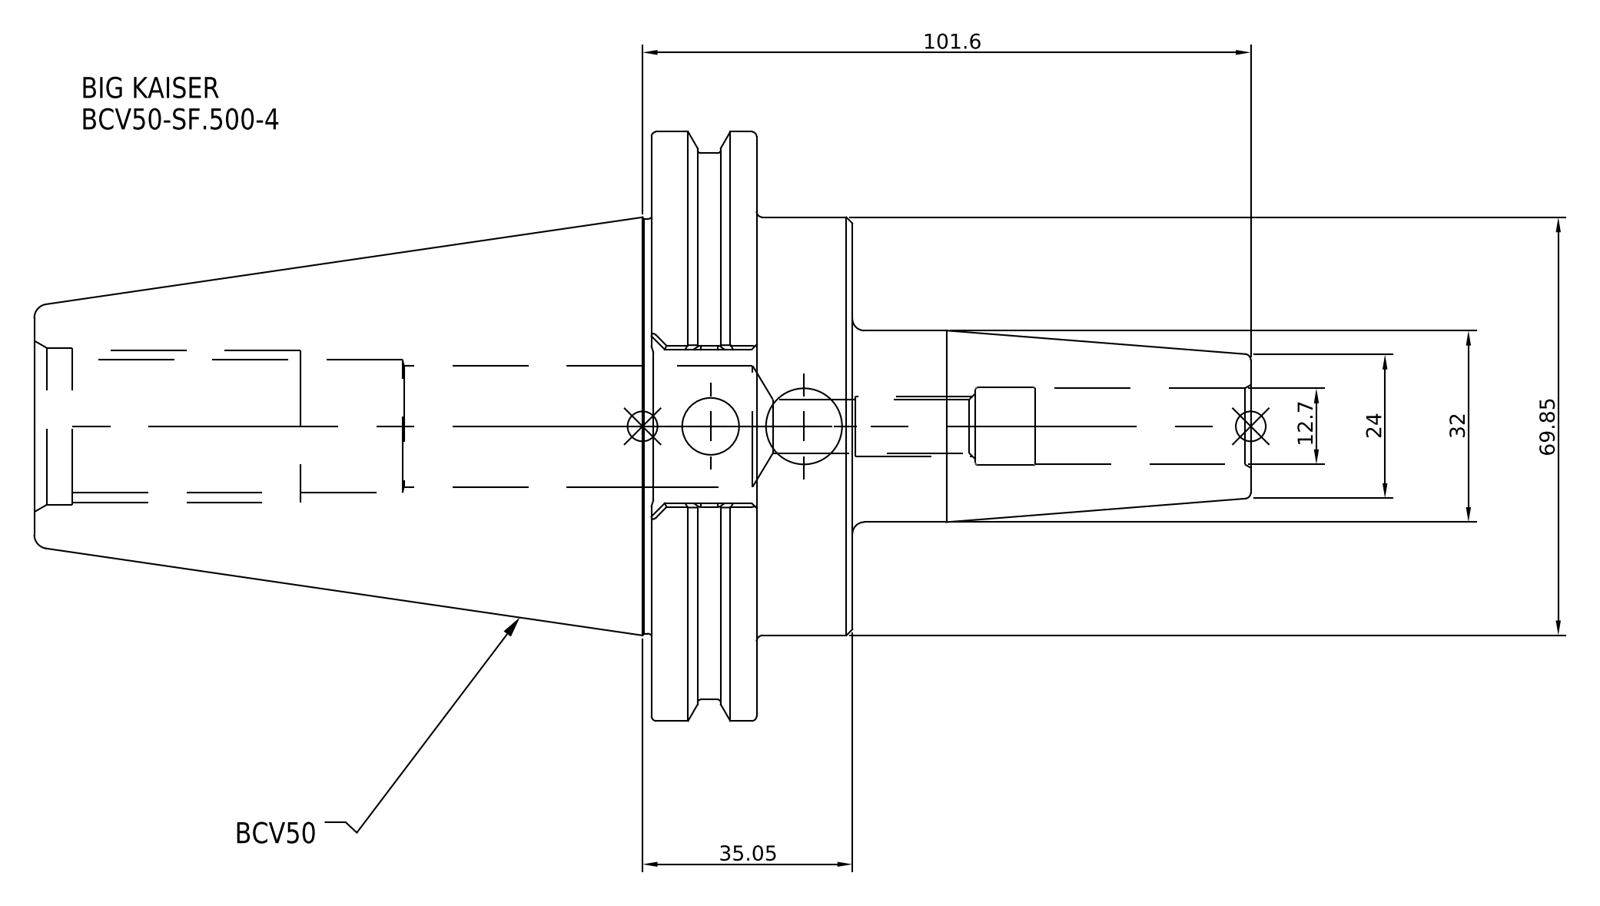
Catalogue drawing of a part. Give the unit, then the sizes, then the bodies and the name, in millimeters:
Units: millimetres
Overall size (bounding box): 203.2 × 98.43 × 98.43
Round holes (diameter × count): ⌀12.7 ×1
Round bosses / shafts (diameter × count): ⌀98.43 ×1, ⌀91.29 ×1, ⌀69.85 ×1, ⌀32 ×1
Main face-to-face distances: 17.55, 16, 33.55, 136.65, 120.65, 103.1, 66.55, 82.55, 100.1, 203.2
Volume: 482 267 mm³ · Surface area: 48 134 mm²
Bodies: 1 solid, 30 faces (8 planar, 14 cylindrical, 8 other)
Part name (STEP PRODUCT): BCV50-SF_500-4
STEP written by: SolidWorks 2021 (CONFIG_CONTROL_DESIGN)
